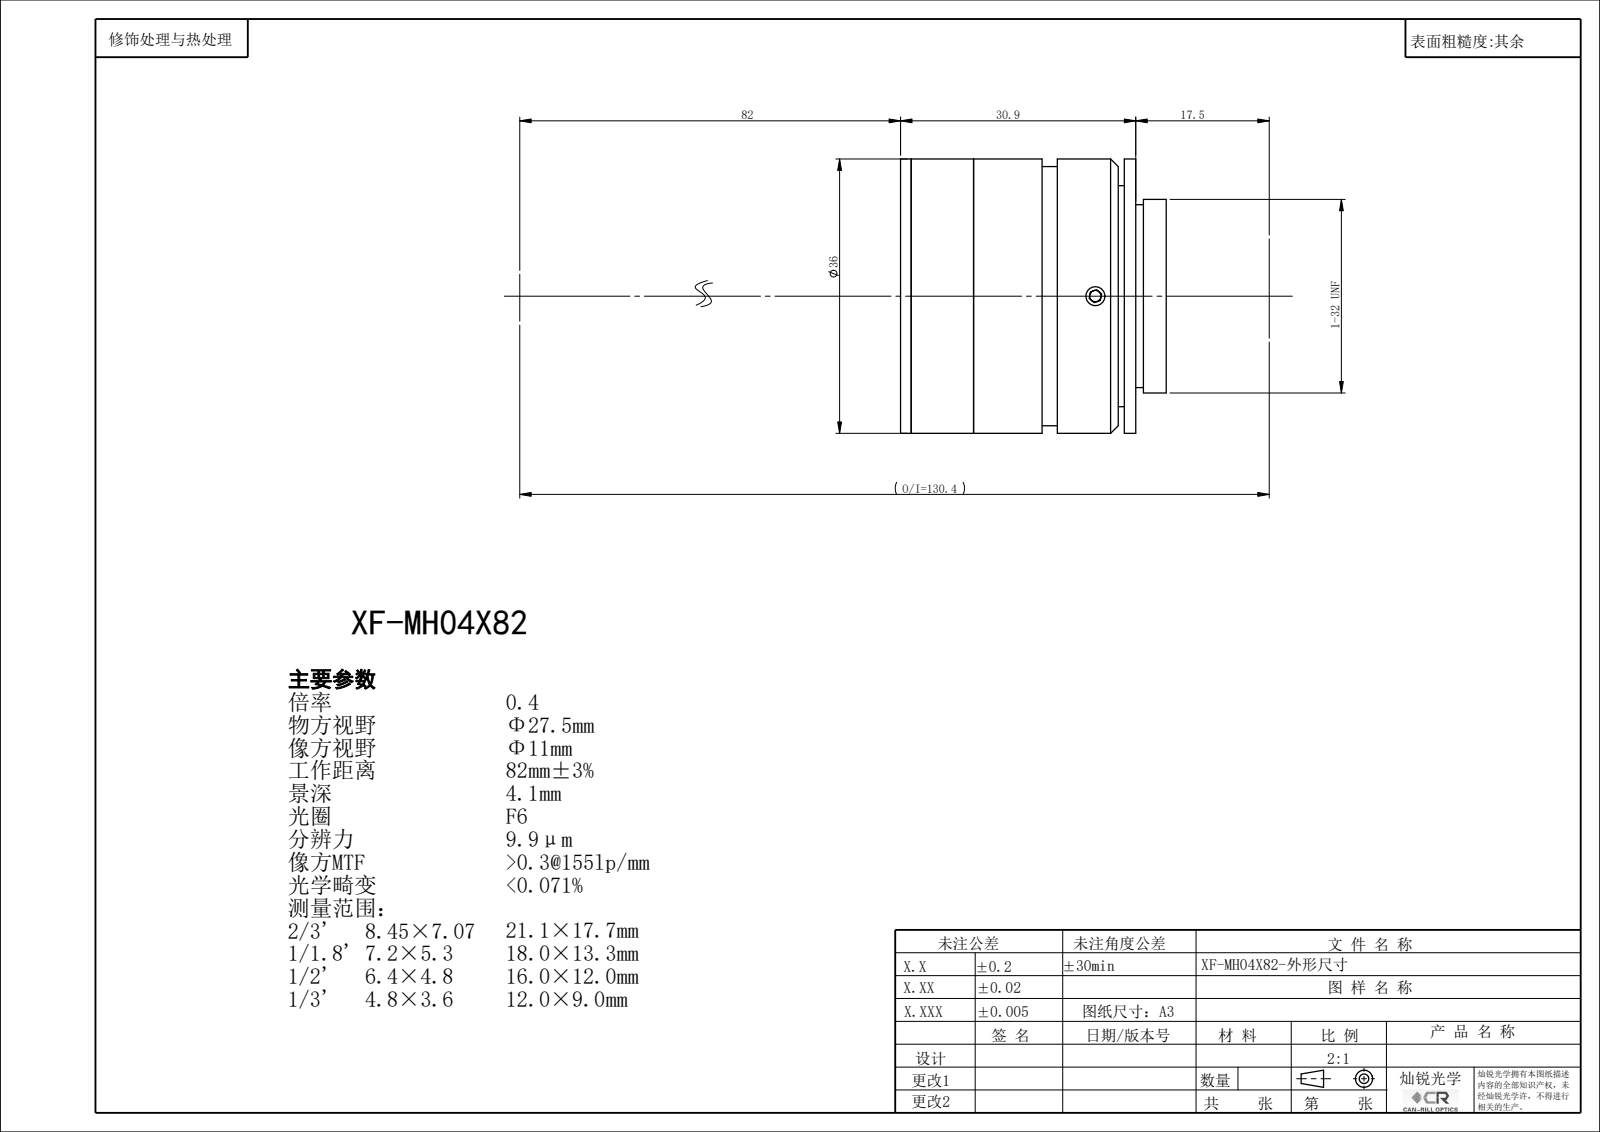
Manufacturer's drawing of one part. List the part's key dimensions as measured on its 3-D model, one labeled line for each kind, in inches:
Part name (STEP PRODUCT): XF-MH04X82-ST
STEP written by: SolidWorks 2022 (CONFIG_CONTROL_DESIGN)
Units: inches
Bodies: 14 solids, 244 faces (96 planar, 108 cylindrical, 40 other)
Overall size (bounding box): 1.417 × 1.417 × 1.373
Volume: 1.496 in³ · Surface area: 32.02 in²
Round holes (diameter × count): ⌀0.098 ×3, ⌀0.079 ×2, ⌀0.201 ×1, ⌀0.276 ×1, ⌀0.315 ×1, ⌀0.354 ×1, ⌀0.409 ×1, ⌀0.472 ×1, ⌀0.512 ×1, ⌀0.669 ×1, ⌀0.787 ×1, ⌀0.827 ×1
Round bosses / shafts (diameter × count): ⌀0.118 ×3, ⌀1.417 ×1, ⌀1.339 ×1, ⌀1.181 ×1, ⌀1.102 ×1, ⌀1.063 ×1, ⌀1 ×1, ⌀0.945 ×1
Main face-to-face distances: 0.055, 0.693, 0.322, 0.839, 0.157, 1.161, 0.378, 1.216, 0.315, 0.276
Hole centre spacings: 0.472, 0.945
